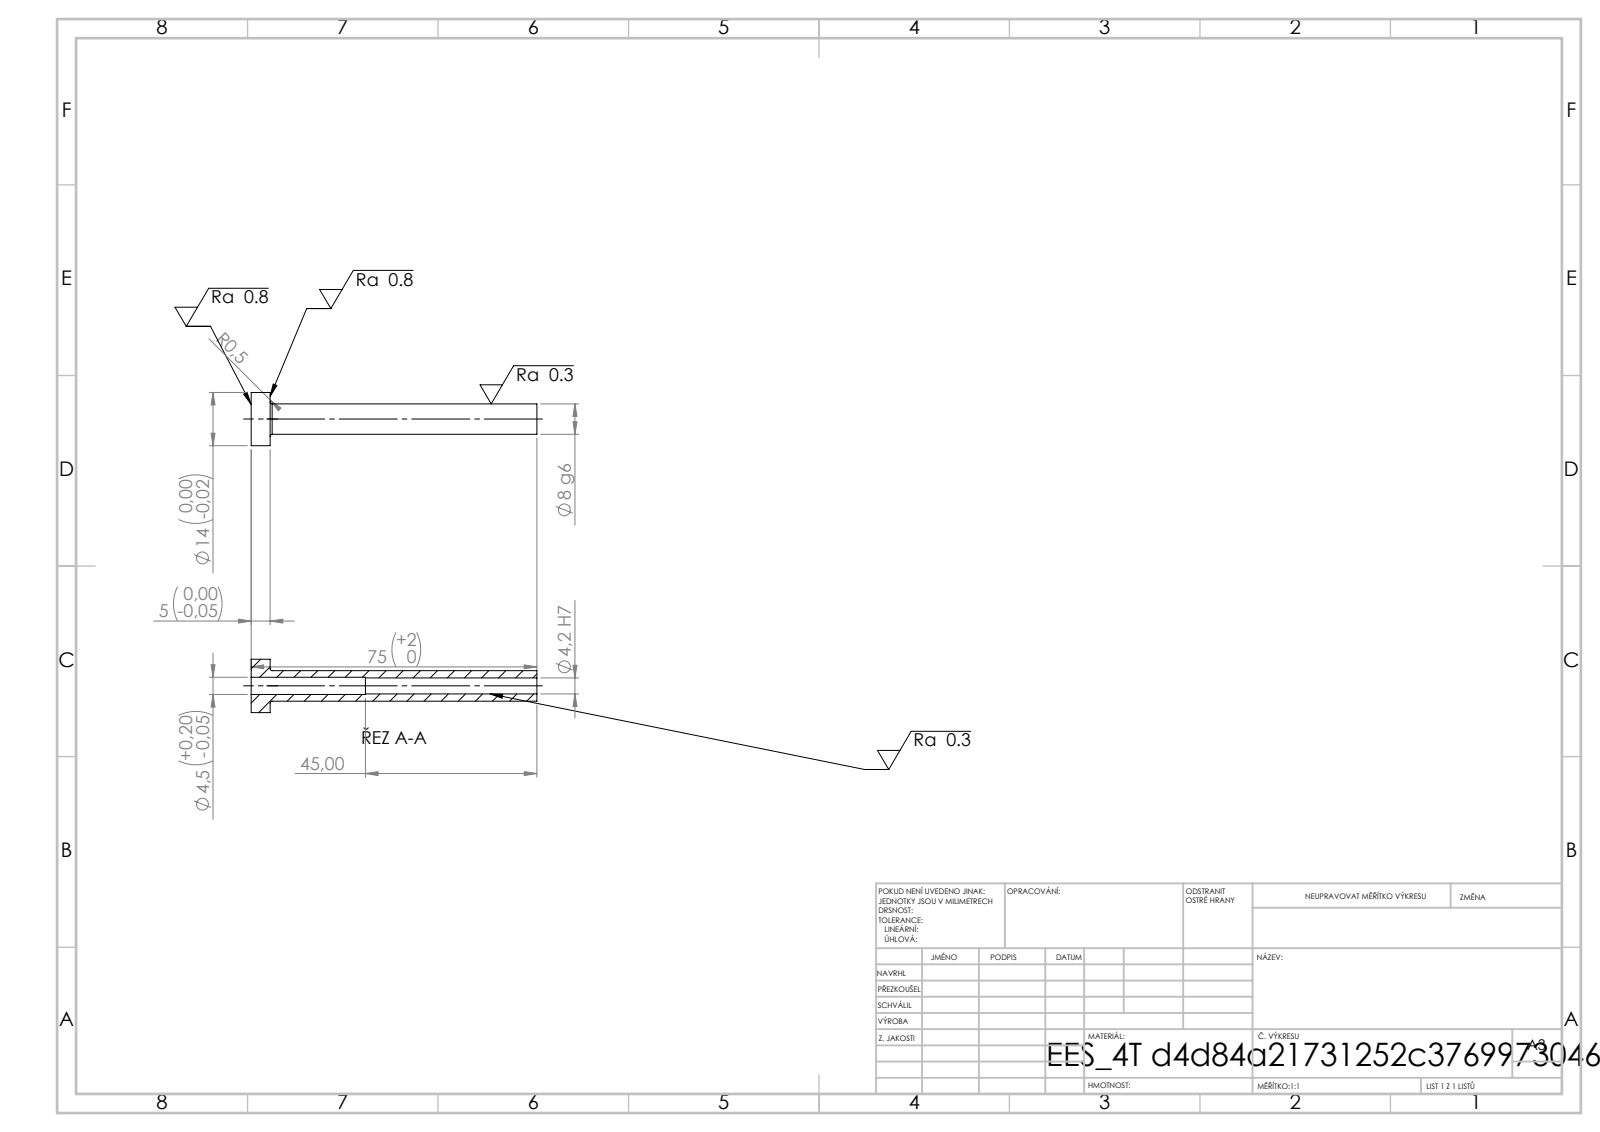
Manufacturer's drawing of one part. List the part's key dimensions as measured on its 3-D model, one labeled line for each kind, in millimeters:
STEP written by: SolidWorks 2019 (CONFIG_CONTROL_DESIGN)
Units: millimetres
Bodies: 1 solid, 14 faces (4 planar, 8 cylindrical, 2 other)
Overall size (bounding box): 75 × 14 × 14
Volume: 3 189 mm³ · Surface area: 3 272 mm²
Round holes (diameter × count): ⌀4.2 ×1, ⌀4.5 ×1
Round bosses / shafts (diameter × count): ⌀14 ×1, ⌀8 ×1
Main face-to-face distances: 5, 75, 70, 30, 25, 45
